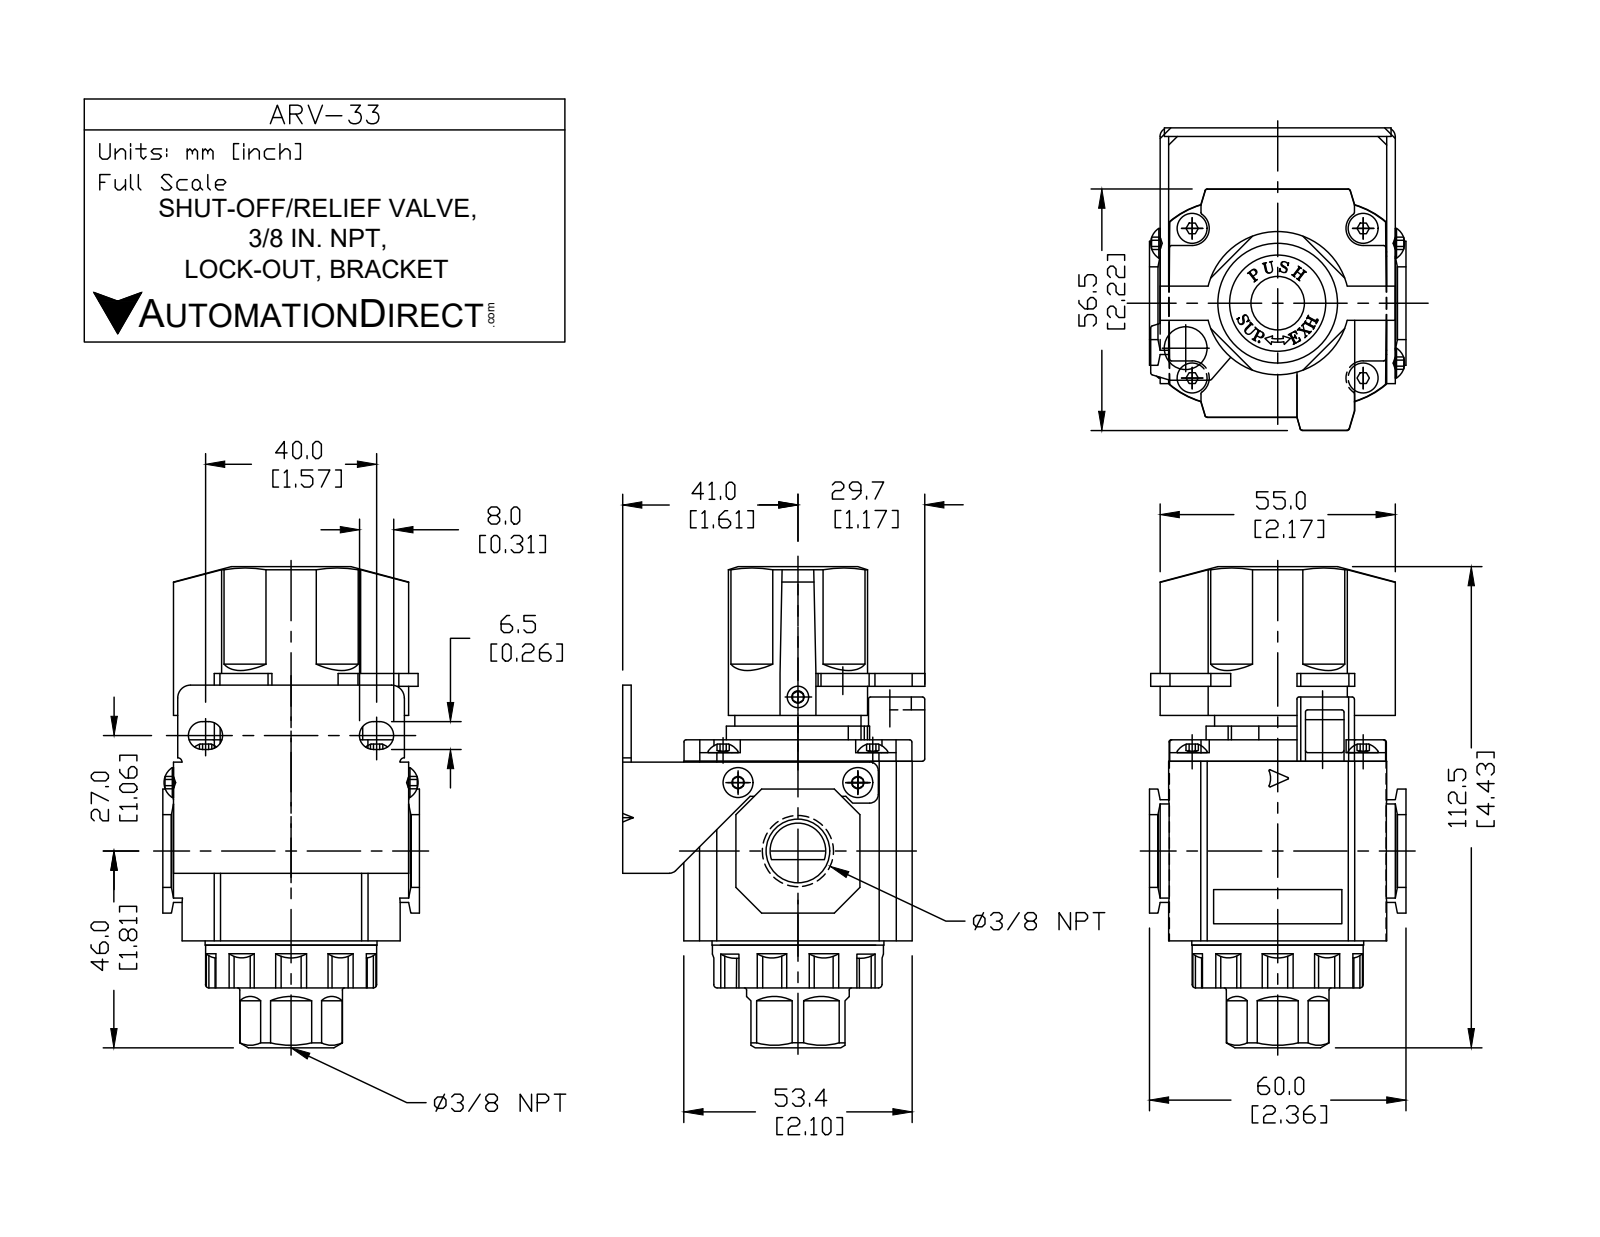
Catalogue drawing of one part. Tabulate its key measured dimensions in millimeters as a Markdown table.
| quantity | value |
| --- | --- |
| part name | ARV-33 |
| STEP written by | SolidWorks 2015 (CONFIG_CONTROL_DESIGN) |
| units | millimeters |
| bodies | 18 solids, 418 faces (290 planar, 83 cylindrical, 45 other) |
| overall size | 112.5 × 70.7 × 60.97 |
| volume | 189 350 mm³ |
| surface area | 48 550 mm² |
| round holes (diameter × count) | 10 × 1, 14.27 × 1, 23.45 × 1 |
| round bosses / shafts (diameter × count) | 7 × 6, 40 × 1, 39.2 × 1, 33.5 × 1, 24.2 × 1, 16.75 × 1 |
| partial cylindrical surfaces (radius × count) | 1.5 × 6, 3.25 × 4, 4.9 × 4, 1 × 2, 2 × 2, 3 × 2, 5 × 1, 11.88 × 1 |
| main face-to-face distances | 2, 42, 4.1, 46.1, 53, 51, 14.3, 67.7, 12.3, 65.7 |
| hole center spacings | 23.93 |
